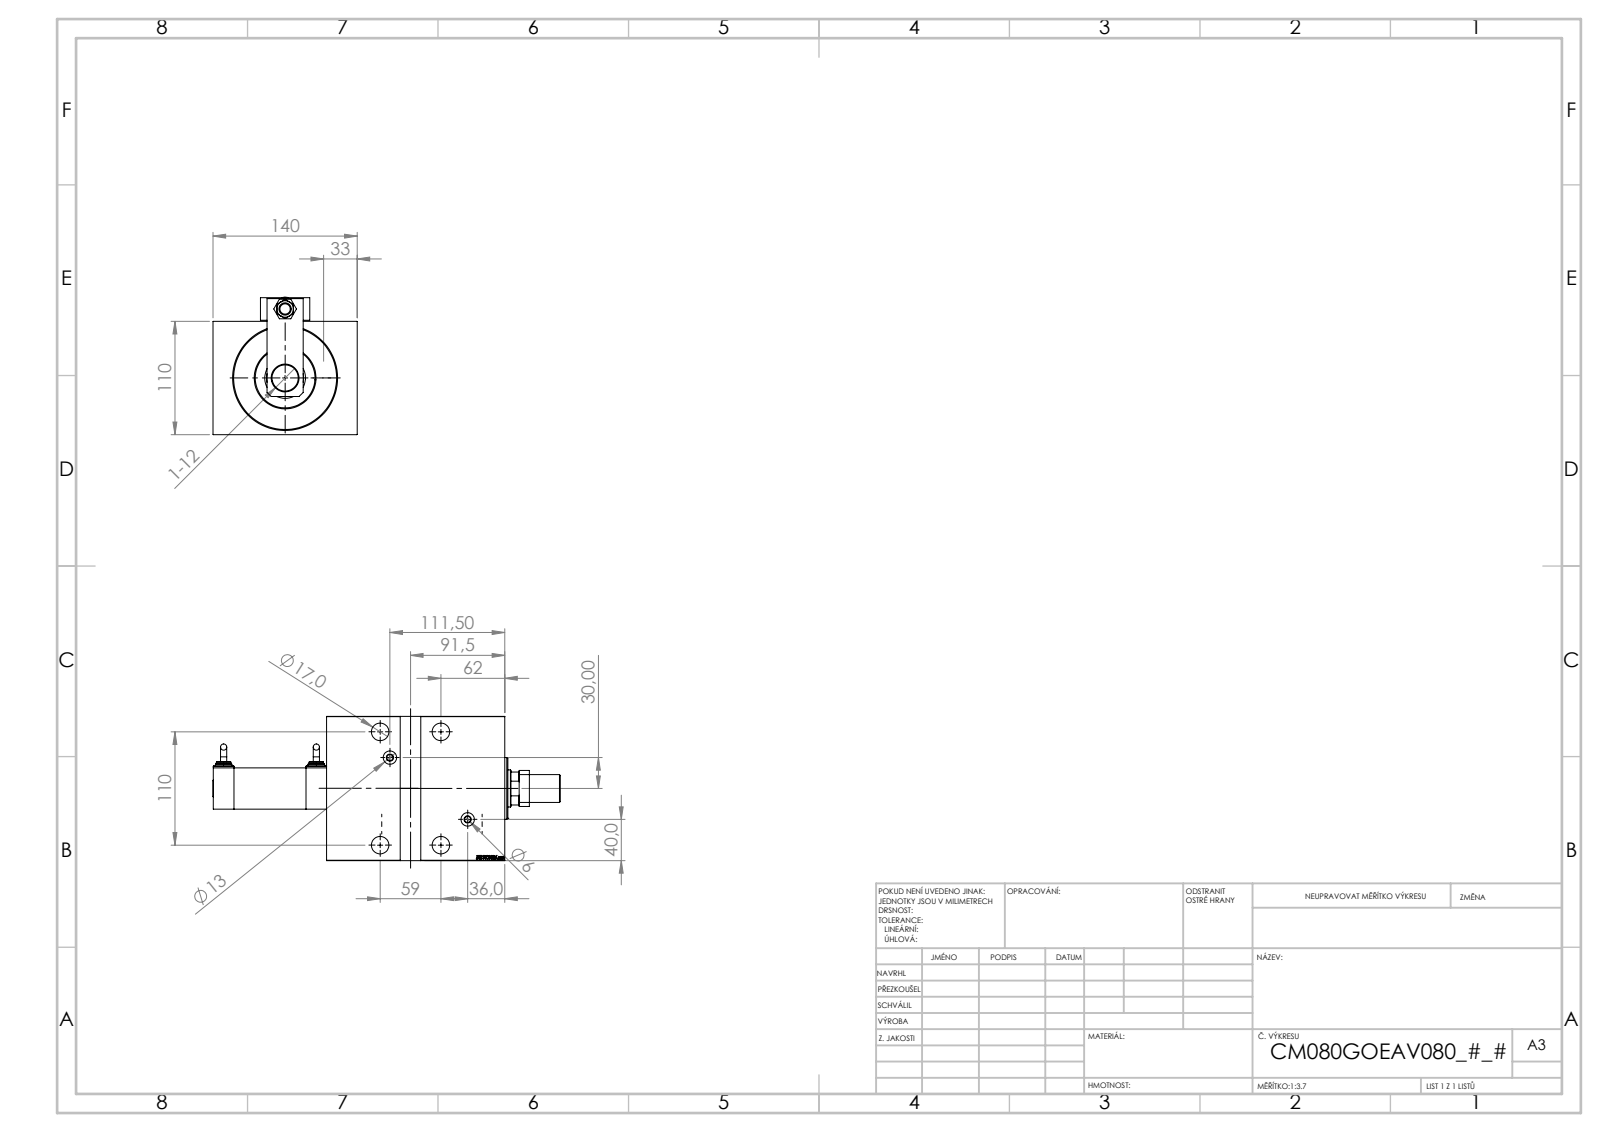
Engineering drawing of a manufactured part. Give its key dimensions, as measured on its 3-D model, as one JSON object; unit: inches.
{"part_name": "KROUZEK_PRO_TYC; SWITCH_P_FRONT_BACK; V450CM_G_VCP; V450CM_MALE_METRIC (+7 more)", "step_written_by": "SolidWorks 2019 (CONFIG_CONTROL_DESIGN)", "units": "inches", "bodies": {"solids": 17, "faces": 1135, "planar": 558, "cylindrical": 118, "other": 459}, "overall_size": [13.28, 5.512, 5.256], "volume_in3": 151.2, "surface_area_in2": 482.2, "round_holes": [[0.157, 4], [0.315, 4], [0.669, 4], [0.984, 4], [0.512, 3], [0.236, 2], [0.472, 1], [0.551, 1], [1.004, 1], [1.063, 1], [1.417, 1], [1.555, 1]], "round_bosses_or_shafts": [[0.787, 3], [1.024, 2], [0.63, 2], [0.551, 2], [0.276, 2], [0.236, 2], [2.362, 1], [0.984, 1]], "partial_cylinders_radius": [[0.118, 1], [0.689, 1]], "face_to_face_distances": [4.331, 5.512, 6.811, 0.197, 0.827, 3.543, 5.984, 6.614, 5.787, 1.969], "hole_center_spacings": [0.787, 2.323, 2.492, 2.783, 3.101, 3.339, 4.331, 4.443]}
